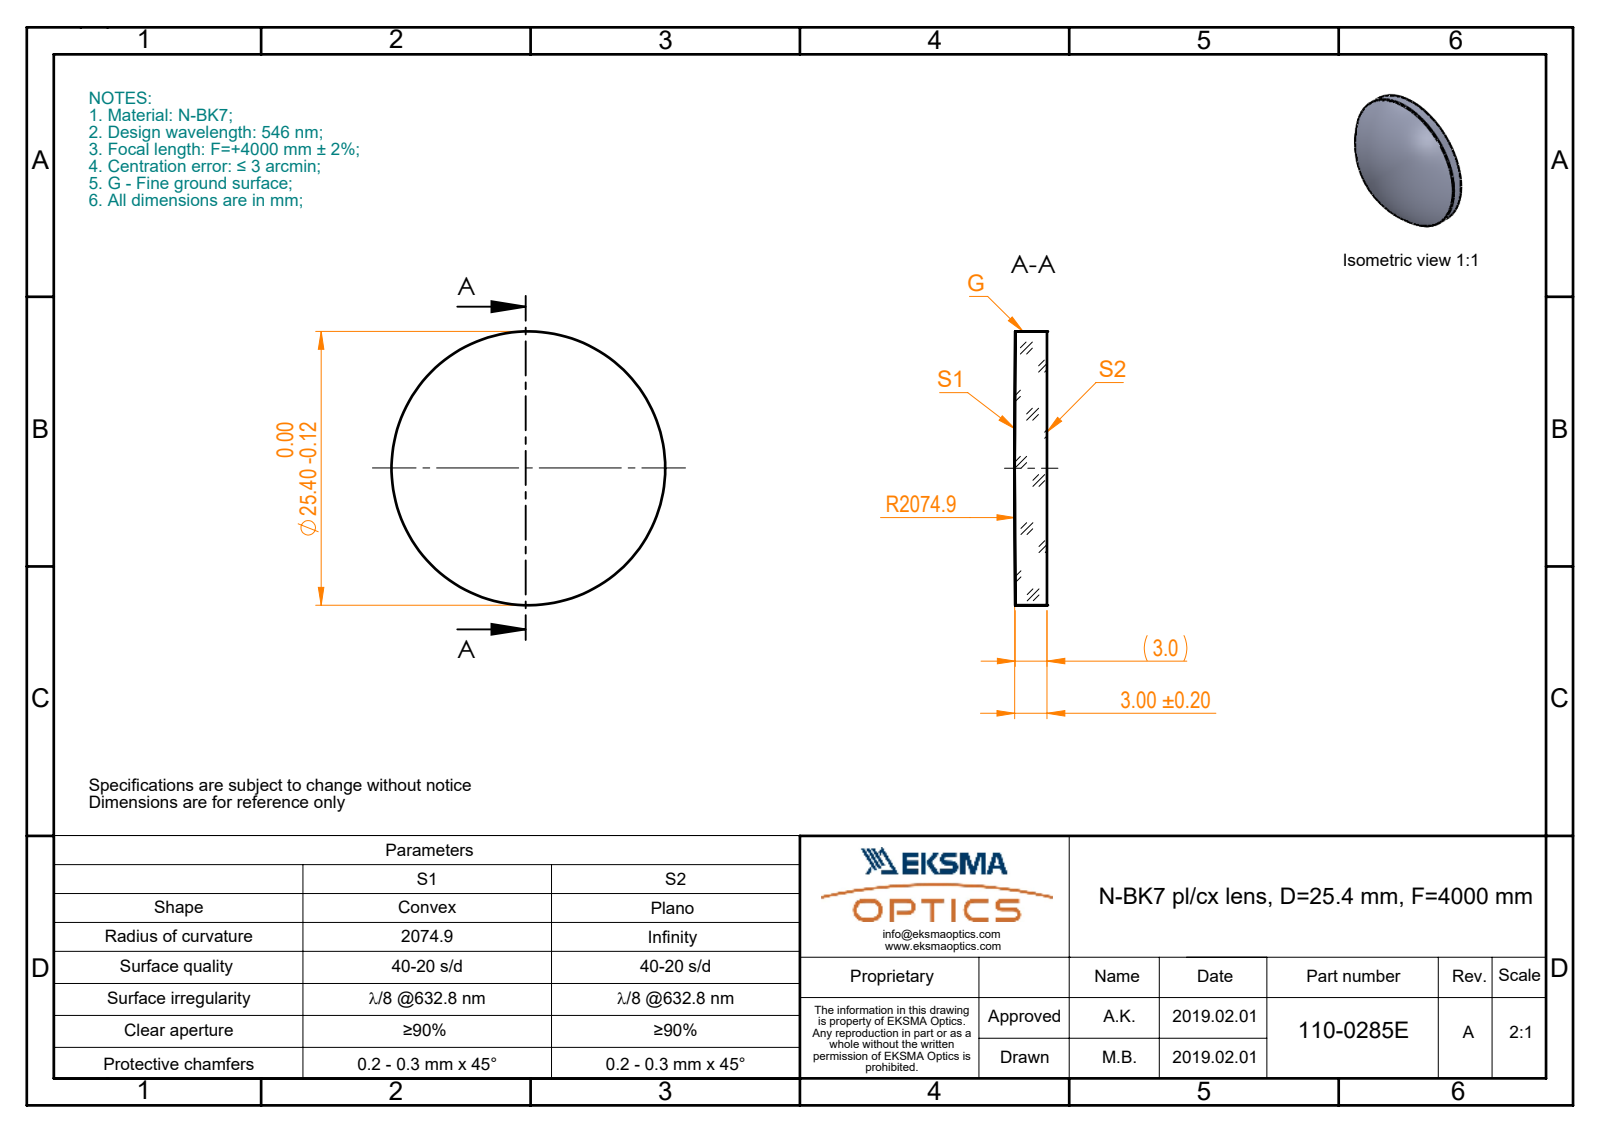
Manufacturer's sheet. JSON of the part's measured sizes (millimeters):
{"part_name": "110-0285E BK7 pl-cx 25.4 F4000", "step_written_by": "SolidWorks 2017 (CONFIG_CONTROL_DESIGN)", "units": "millimeters", "bodies": {"solids": 1, "faces": 5, "planar": 1, "cylindrical": 2, "other": 2}, "overall_size": [25.4, 25.4, 3], "volume_mm3": 1510, "surface_area_mm2": 1250, "round_bosses_or_shafts": [[25.4, 1]]}
